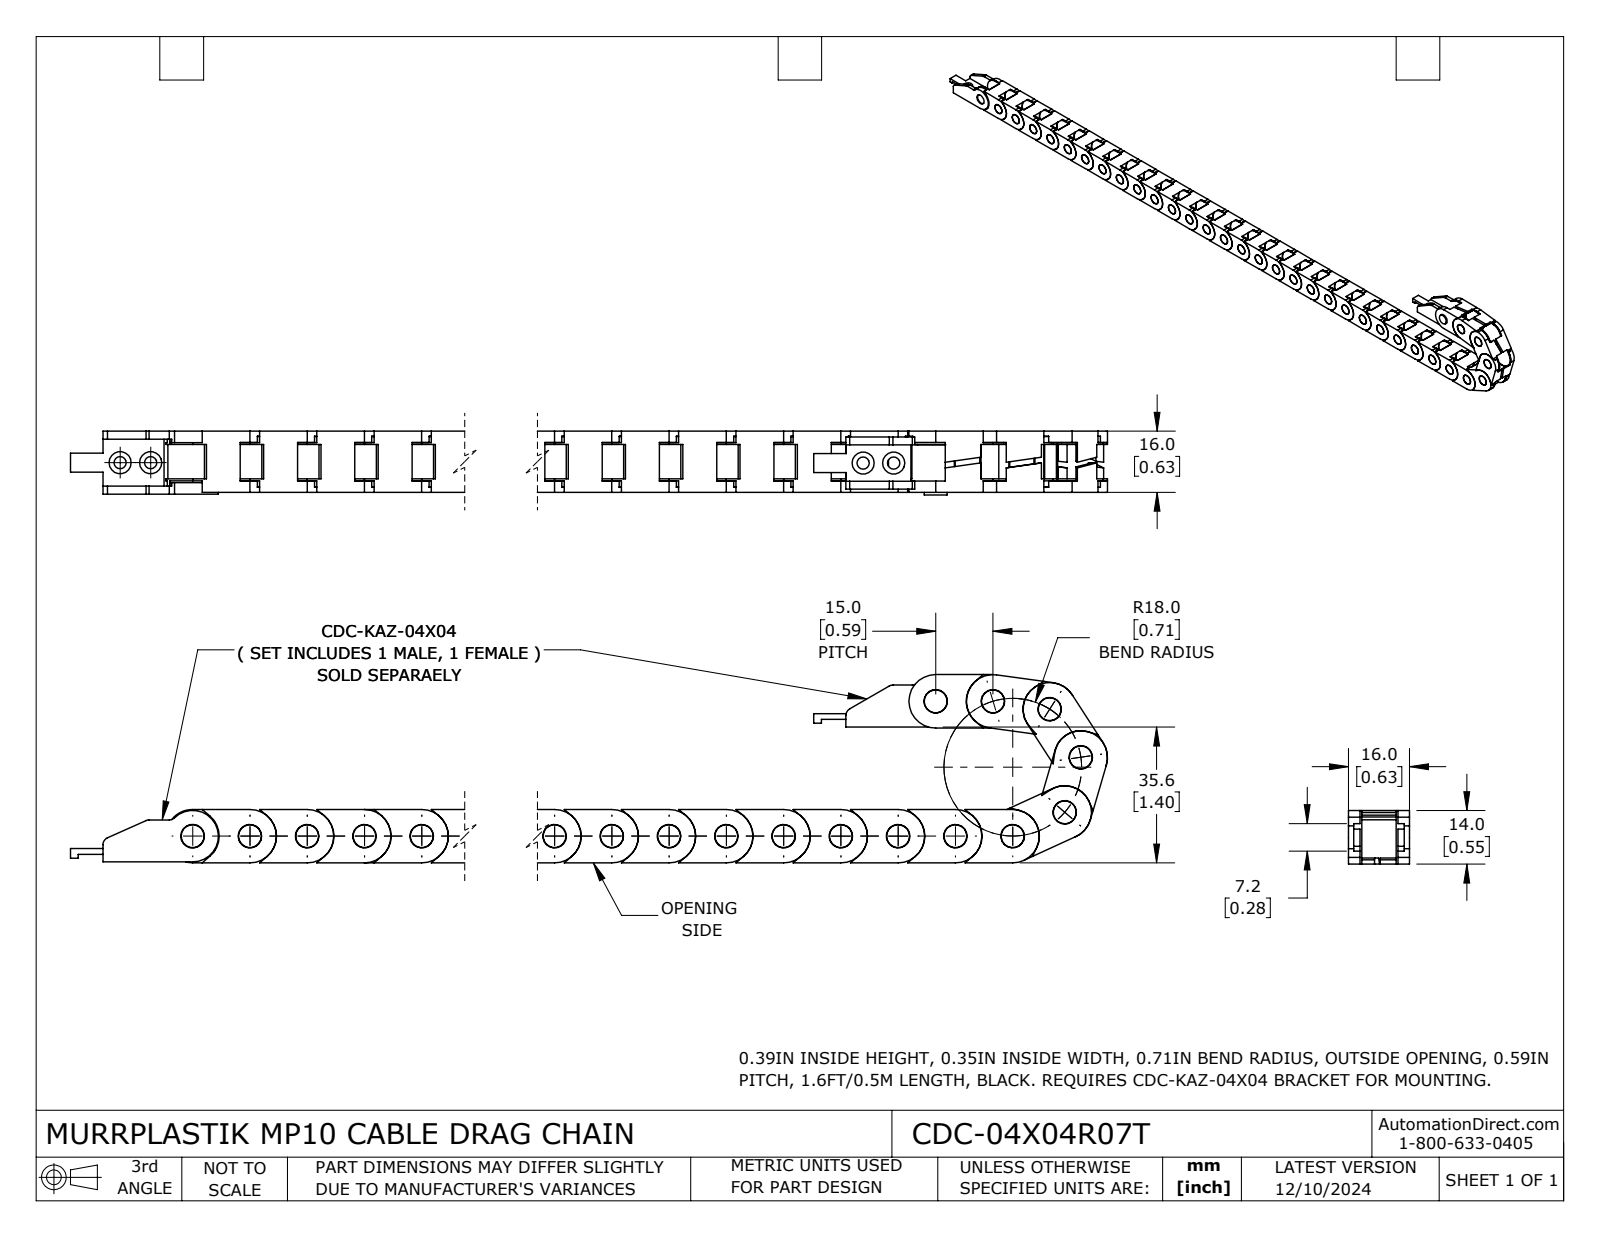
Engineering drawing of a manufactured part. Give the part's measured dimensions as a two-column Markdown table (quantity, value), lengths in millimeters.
| quantity | value |
| --- | --- |
| part name | CDC-04X04R07T |
| STEP written by | SolidWorks 2024 (AUTOMOTIVE_DESIGN) |
| units | millimeters |
| bodies | 34 solids, 2304 faces (1560 planar, 740 cylindrical, 4 other) |
| overall size | 476.8 × 49.3 × 16.7 |
| volume | 55 160 mm³ |
| surface area | 78 320 mm² |
| round holes (diameter × count) | 6.1 × 32, 3.2 × 4, 6.2 × 1 |
| round bosses / shafts (diameter × count) | 6 × 33, 14 × 31 |
| partial cylindrical surfaces (radius × count) | 0.5 × 160, 7 × 33, 3.6 × 32, 11.6 × 32, 2 × 6, 1 × 2, 6.8 × 2, 7 × 2 |
| main face-to-face distances | 3.5, 12.5, 9, 16, 2.2, 1.6, 0.5, 1.3, 11.7, 13 |
| hole center spacings | 15, 30, 45, 60, 75, 90, 105, 120 |
